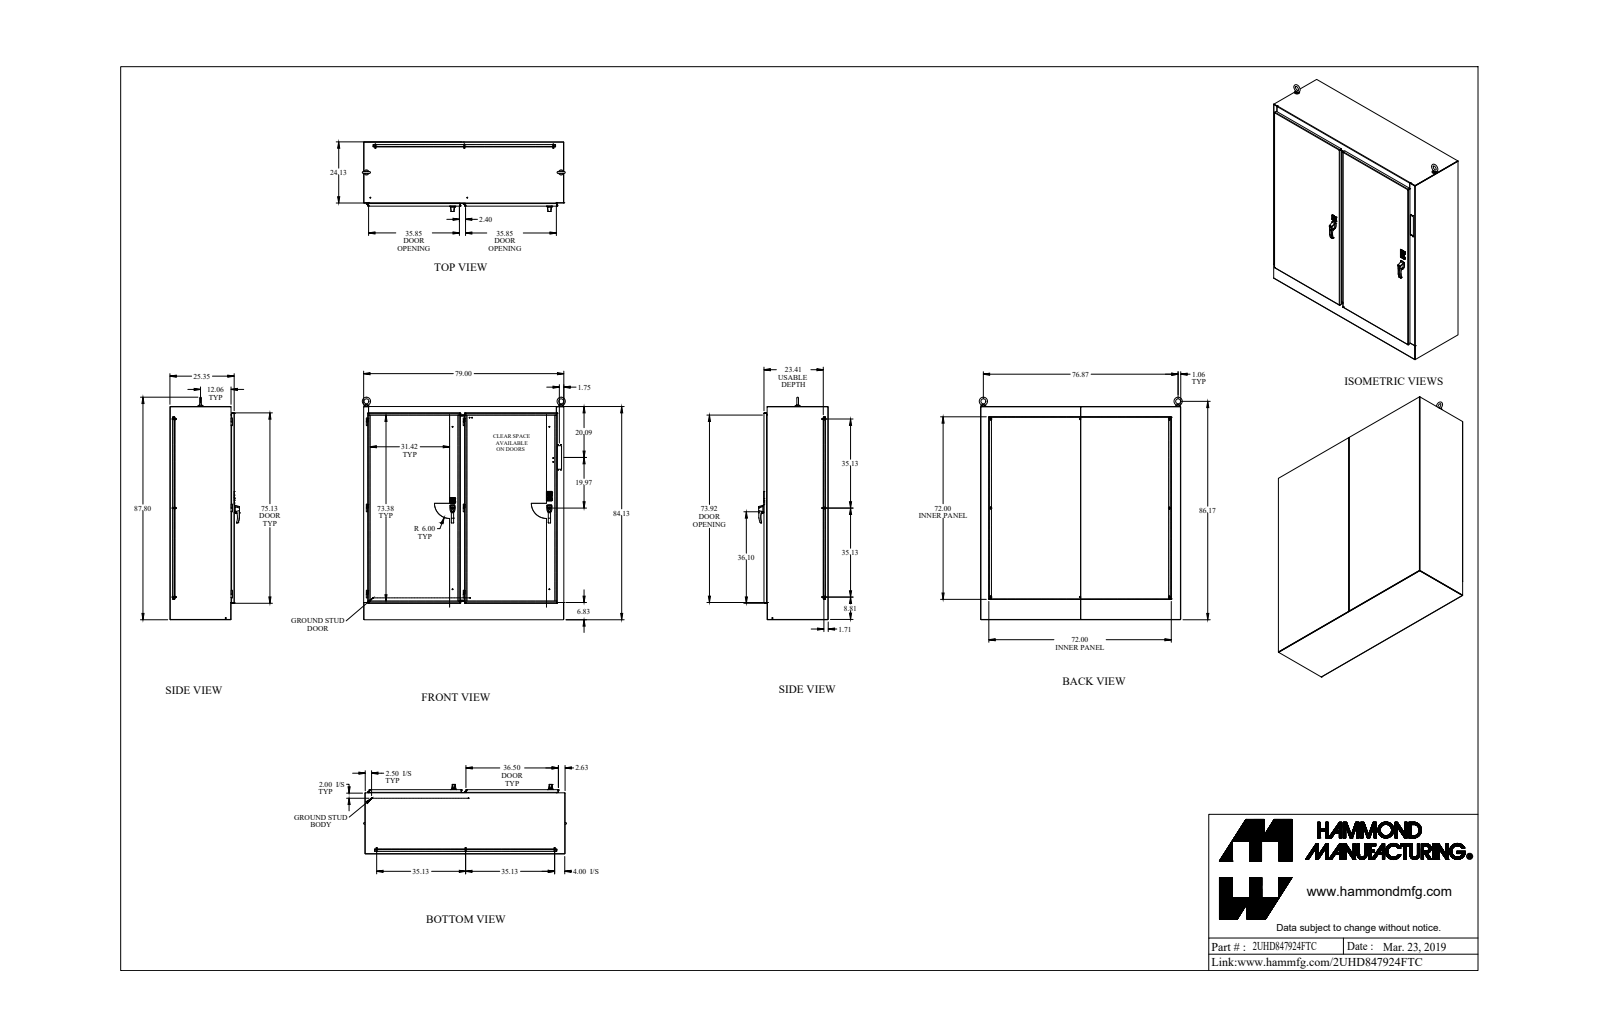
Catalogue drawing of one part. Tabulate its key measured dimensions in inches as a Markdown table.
| quantity | value |
| --- | --- |
| part name | 2UHD847924FTC |
| STEP written by | SolidWorks 2018 (AUTOMOTIVE_DESIGN) |
| units | inches |
| bodies | 217 solids, 3088 faces (1806 planar, 908 cylindrical, 374 other) |
| overall size | 87.799 × 80.122 × 27.466 |
| volume | 5 798 in³ |
| surface area | 61 902 in² |
| round holes (diameter × count) | 0.196 × 12, 0.281 × 11, 0.307 × 11, 0.25 × 10, 0.35 × 8, 0.257 × 6, 0.313 × 6, 0.445 × 5, 0.28 × 4, 0.282 × 4, 0.375 × 4, 0.39 × 4 |
| round bosses / shafts (diameter × count) | 0.25 × 19, 1 × 12, 0.65 × 9, 0.375 × 9, 0.33 × 9, 0.625 × 8, 0.281 × 8, 0.75 × 6 |
| partial cylindrical surfaces (radius × count) | 0.125 × 62, 0.06 × 55, 0.5 × 42, 0.185 × 34, 0.03 × 28, 0.017 × 16, 0.018 × 16, 0.032 × 12 |
| main face-to-face distances | 0.125, 0.072, 23.431, 0.125, 25.369, 25.243, 1.937, 1.812, 1.865, 1.74 |
| hole center spacings | 38.249, 70.25, 1, 1.126, 1.287, 30.937, 32.063, 32.069 |
